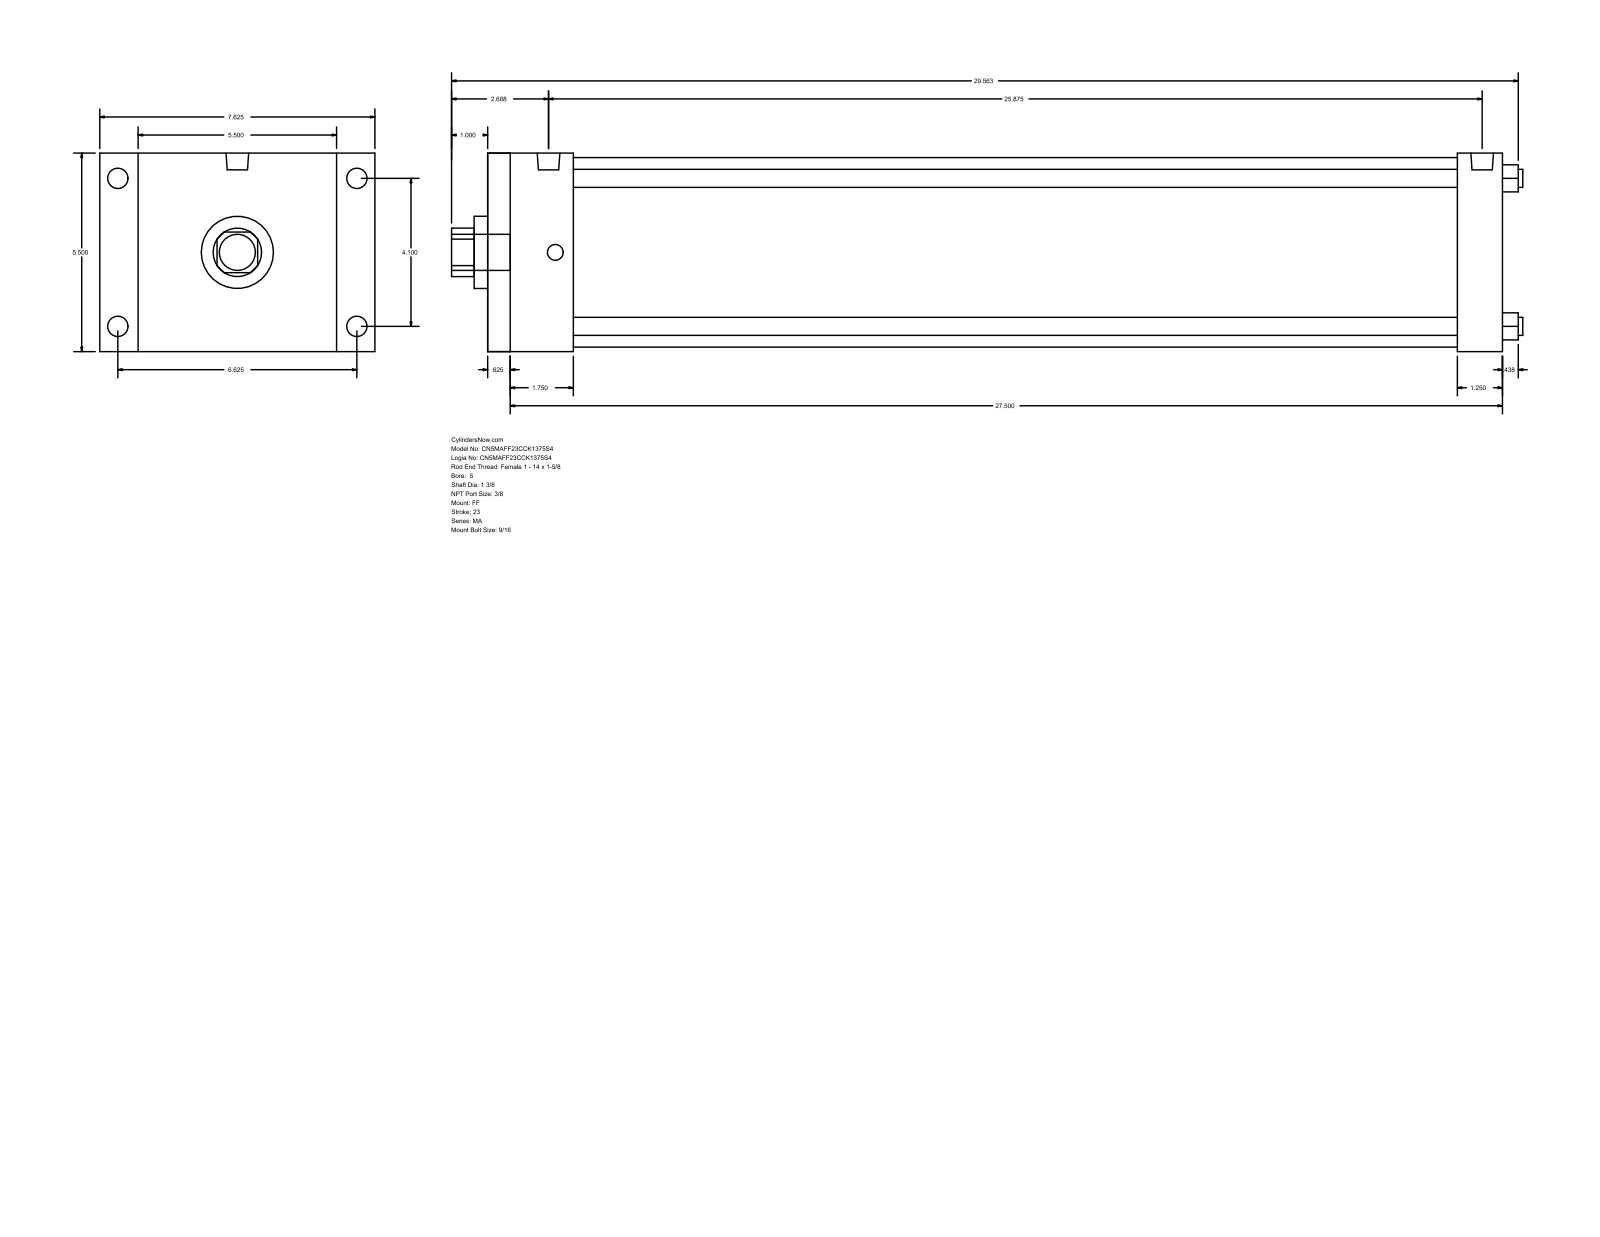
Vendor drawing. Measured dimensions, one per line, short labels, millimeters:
name: MA_FF__0500_1.375
written by: GSSL Pune (CONFIG_CONTROL_DESIGN)
unit: mm
bodies: 0 solids, 92 faces (64 planar, 28 cylindrical, 0 other)
size: 754.06 × 193.68 × 139.7
holes: 4× ⌀12.7, 1× ⌀34.92, 1× ⌀50.8, 1× ⌀133.35
bosses: 4× ⌀14.29, 4× ⌀11.11, 2× ⌀15.93, 1× ⌀25.4
rounds: 1× R17.06
face distances: 139.7, 714.37, 15.87, 698.5, 682.62, 666.75, 31.75, 60.32, 44.45, 622.3
hole spacings: 73.64, 104.14, 147.28
